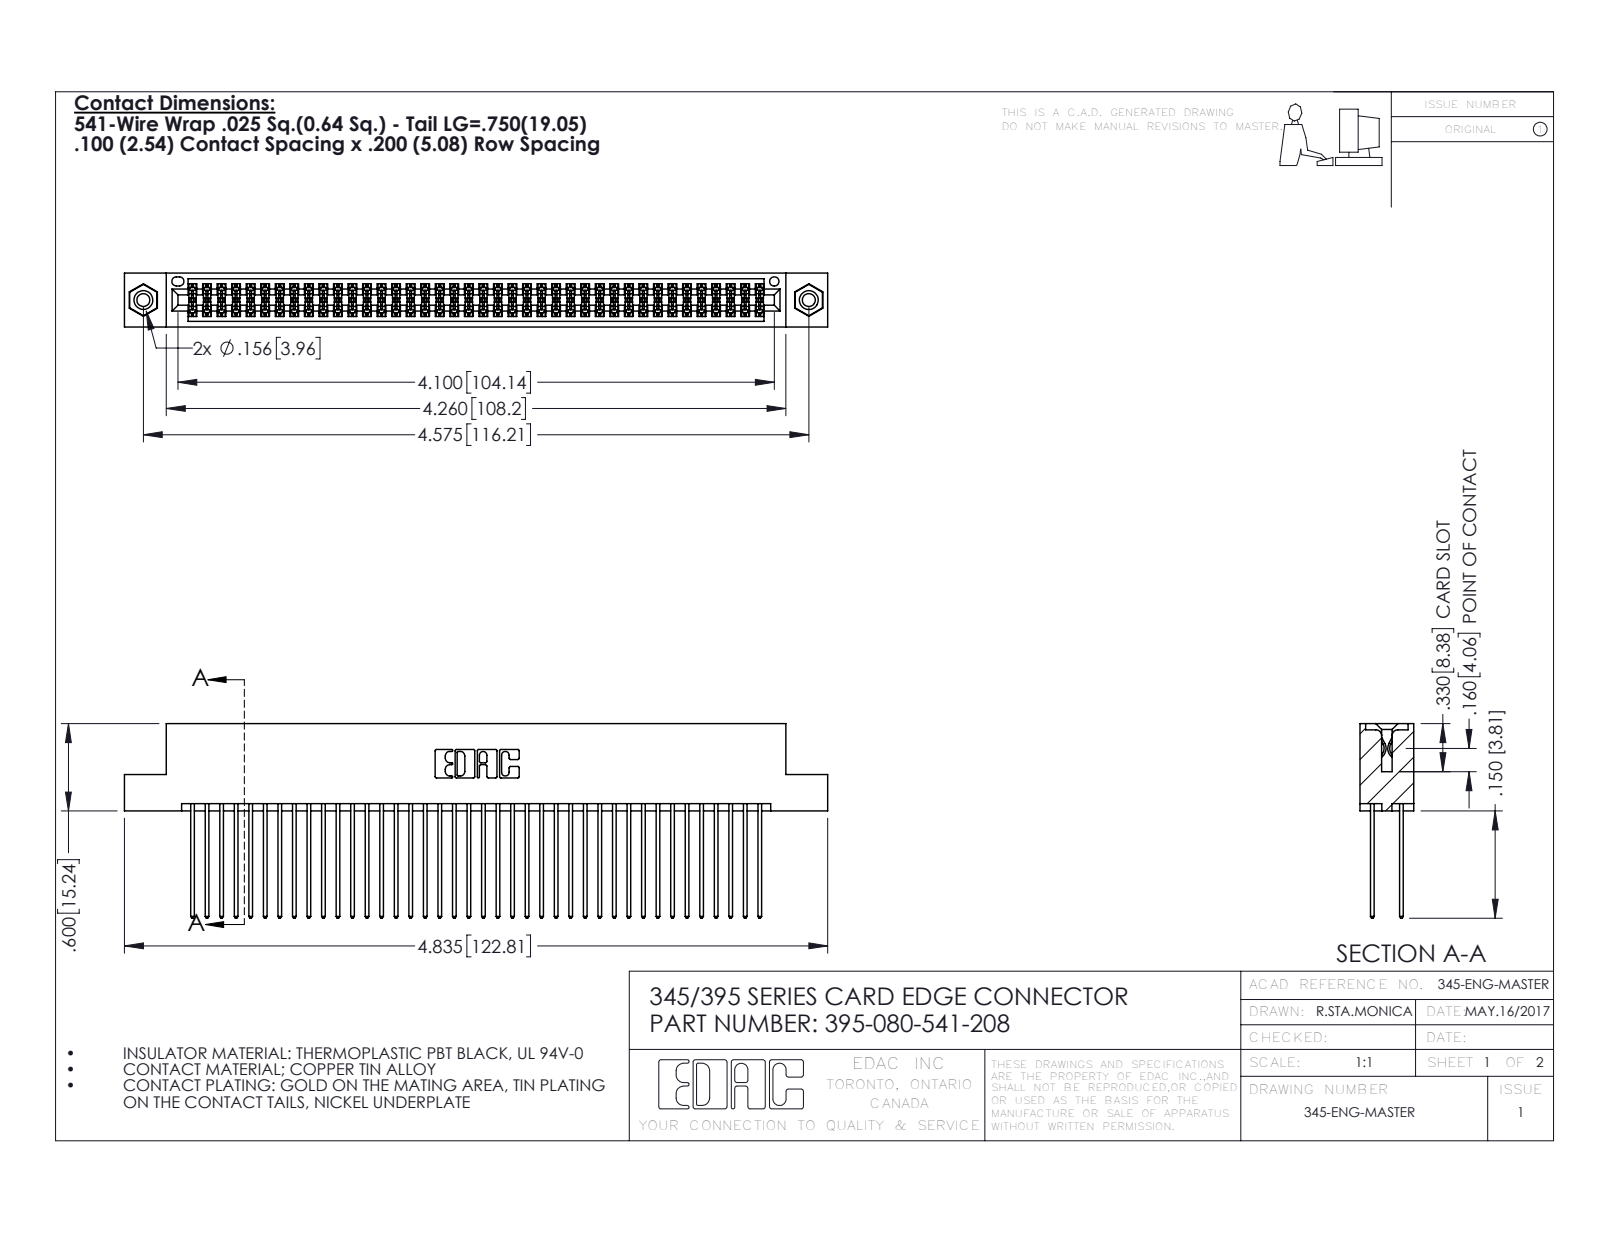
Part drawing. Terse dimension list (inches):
name: 345-292-001_345-293-141; 345-250-001_345-250-003-102; 345 Part_Flush Mounting Lugs - 0.156 Dia-TI; 395-080-541-208
written by: SolidWorks 2016 (CONFIG_CONTROL_DESIGN)
unit: in
bodies: 83 solids, 4186 faces (2752 planar, 1418 cylindrical, 16 other)
size: 4.835 × 1.337 × 0.37
volume: 0.754 in³; area: 31.63 in²
holes: 2× ⌀0.089, 2× ⌀0.125, 2× ⌀0.156, 1× ⌀0.064
bosses: 2× ⌀0.155
rounds: 120× R0.006, 80× R0.01, 22× R0.01, 6× R0.007, 6× R0.031, 3× R0.026, 2× R0.014, 2× R0.019
face distances: 0.072, 0.298, 0.2, 0.098, 0.272, 0.025, 0.225, 0.37, 0.175, 0.149
hole spacings: 0.27, 4.339, 4.575
